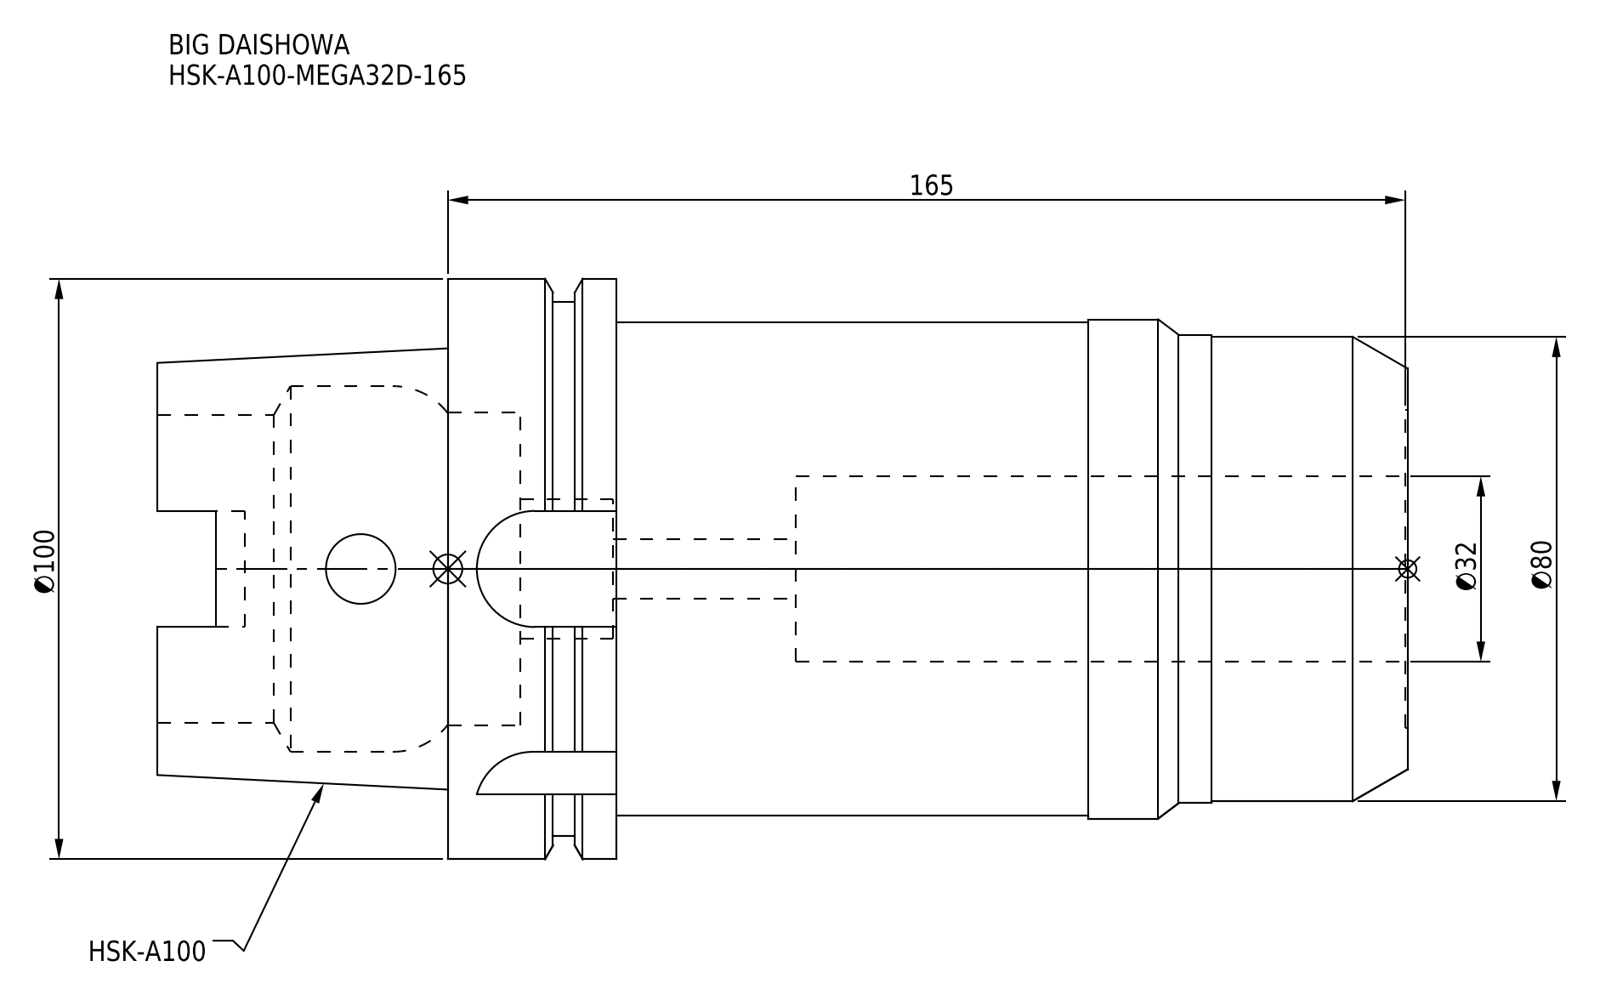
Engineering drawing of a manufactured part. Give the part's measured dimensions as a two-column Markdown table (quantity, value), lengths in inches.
| quantity | value |
| --- | --- |
| part name | HSK-A100-MEGA32D-165 |
| STEP written by | CREO PARAMETRIC BY PTC INC, 2016380 (AUTOMOTIVE_DESIGN) |
| units | inches |
| bodies | 1 solid, 98 faces (36 planar, 44 cylindrical, 18 other) |
| overall size | 8.48 × 3.937 × 3.937 |
| volume | 55.47 in³ |
| surface area | 148.8 in² |
| round holes (diameter × count) | 0.404 × 1, 0.472 × 1, 0.945 × 1, 1.26 × 1, 2.087 × 1, 2.118 × 1, 2.154 × 1, 2.48 × 1 |
| round bosses / shafts (diameter × count) | 3.937 × 1, 3.622 × 1, 3.386 × 1, 3.346 × 1, 3.177 × 1, 3.15 × 1 |
| partial cylindrical surfaces (radius × count) | 0.192 × 4, 0.394 × 4 |
| main face-to-face distances | 1.142, 0.652, 0.49, 5.354, 6.006, 6.496, 0.016, 5.37, 6.022, 6.512 |
